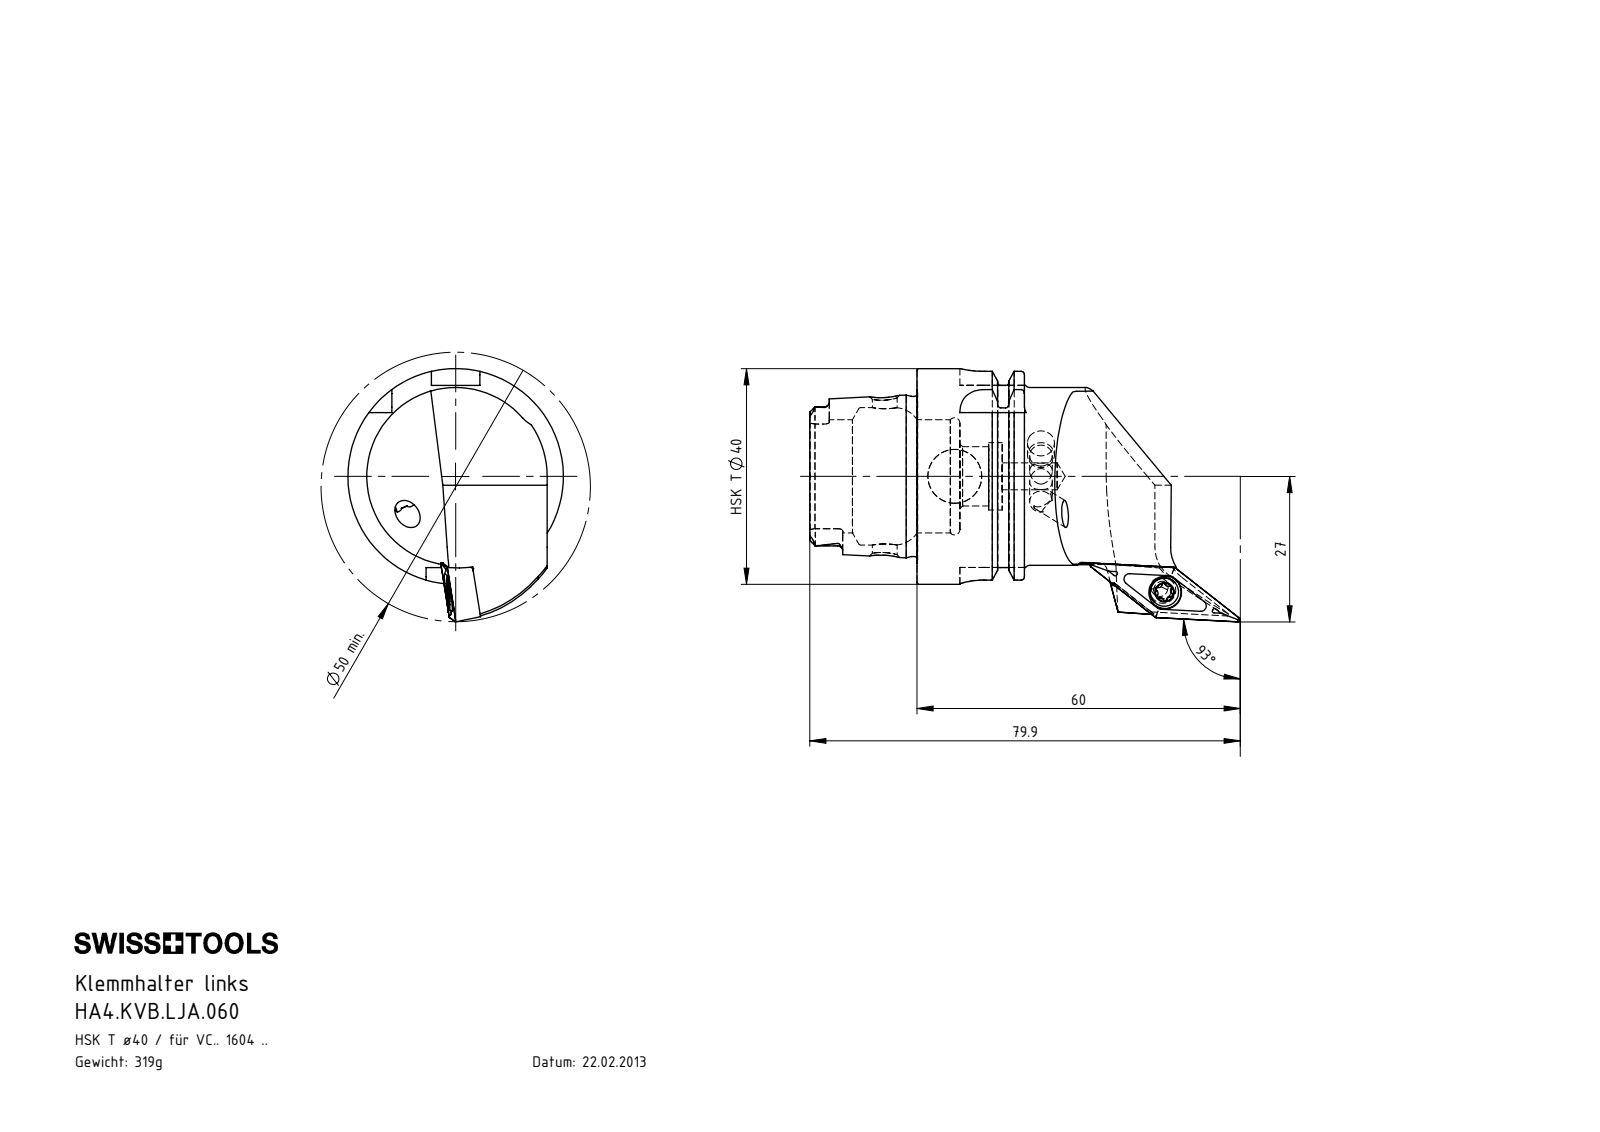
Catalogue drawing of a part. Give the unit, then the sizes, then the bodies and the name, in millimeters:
Units: millimetres
Overall size (bounding box): 79.9 × 47 × 40
Round holes (diameter × count): ⌀4.2 ×2, ⌀5 ×2, ⌀3.3 ×1, ⌀4 ×1, ⌀4.4 ×1, ⌀4.6 ×1, ⌀6.1 ×1, ⌀10 ×1, ⌀11 ×1, ⌀12.5 ×1, ⌀21 ×1, ⌀25.5 ×1
Round bosses / shafts (diameter × count): ⌀40 ×1, ⌀34.75 ×1, ⌀33 ×1, ⌀29.71 ×1, ⌀5.25 ×1, ⌀5 ×1, ⌀4 ×1
Partial cylindrical surfaces — rounded edges, fillets, slot ends (radius × count): R0.34 ×6, R0.59 ×6, R0.9 ×6, R1.88 ×4, R4.5 ×4, R0.8 ×1, R1.75 ×1, R7 ×1
Main face-to-face distances: 7.95, 19.95, 12, 19.9, 27.85, 39.85, 4.43, 4.44, 35.7, 15.8
Volume: 40 208 mm³ · Surface area: 13 803 mm²
Bodies: 5 solids, 321 faces (81 planar, 91 cylindrical, 149 other)
Part name (STEP PRODUCT): KVT_MB_600_050; HA4.KVB.LJA.060; VCMT160404; HA4-KVB.LJA.060_B (+1 more)
STEP written by: SolidWorks 2017 (AUTOMOTIVE_DESIGN)
